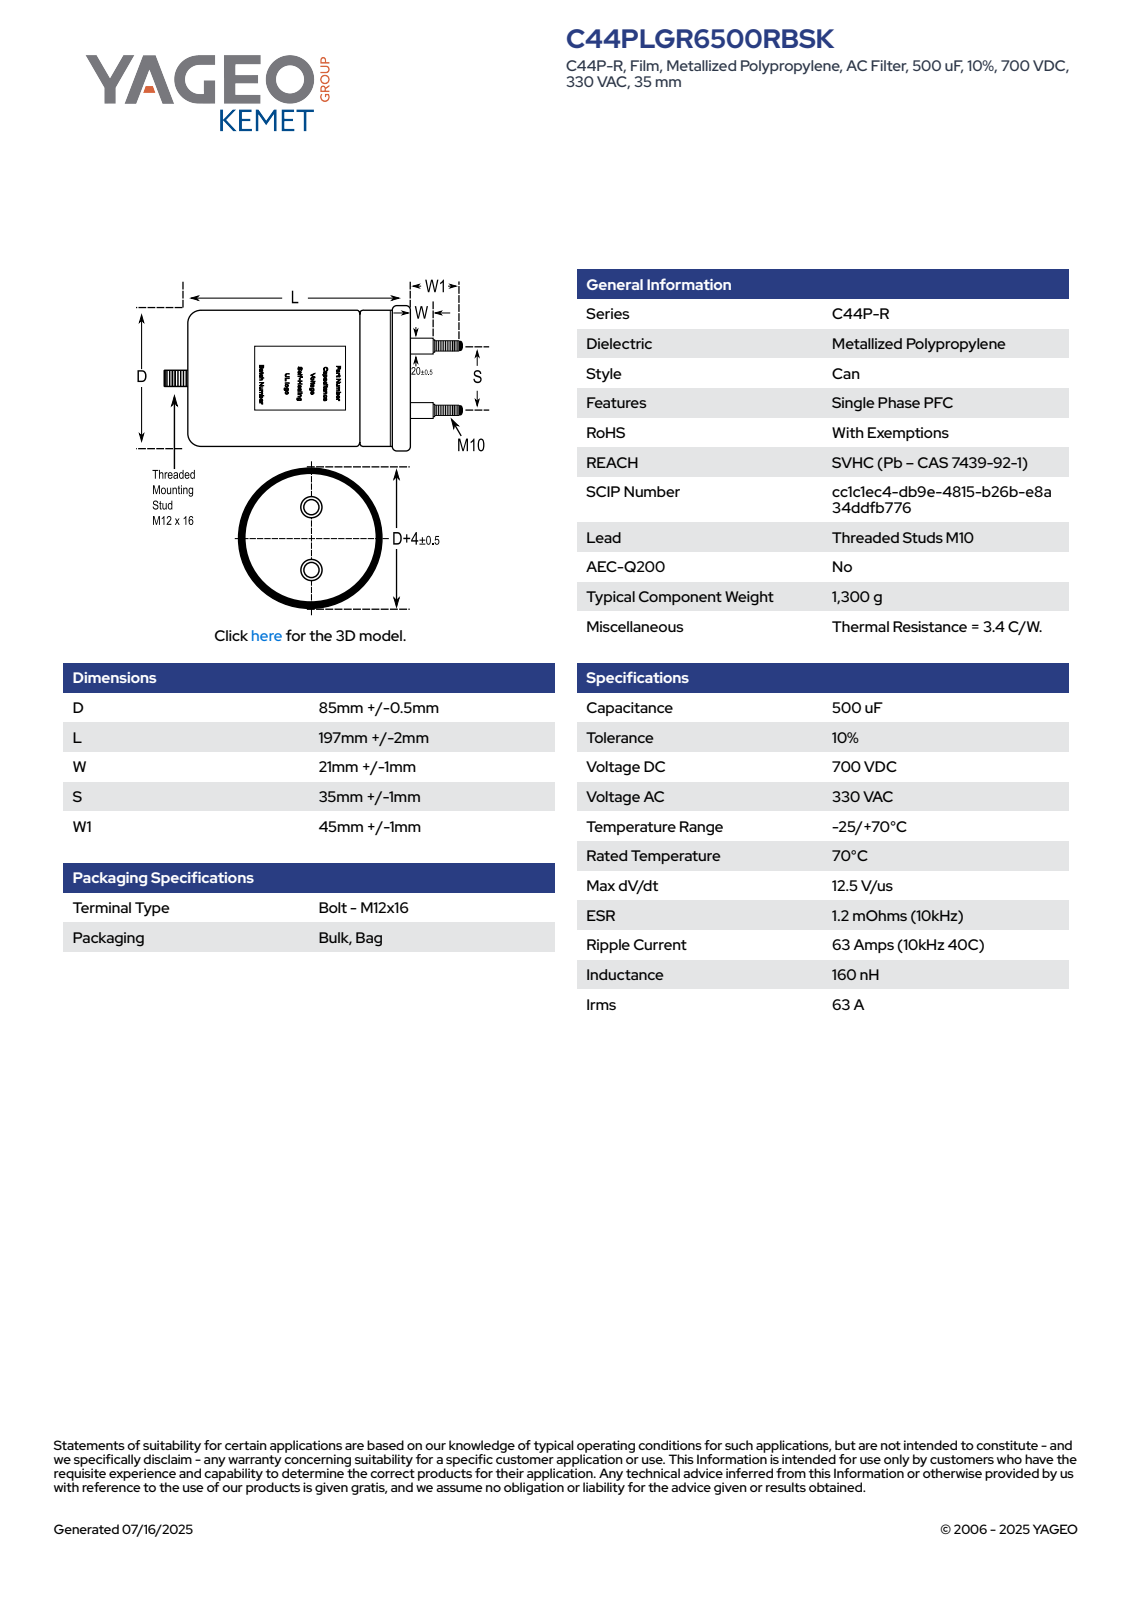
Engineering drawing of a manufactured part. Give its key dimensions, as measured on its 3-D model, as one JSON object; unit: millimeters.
{"part_name": "CFP_C44P_85X197_D85.5L199S35", "step_written_by": "SolidWorks 2014 (AUTOMOTIVE_DESIGN)", "units": "millimeters", "bodies": {"solids": 1, "faces": 105, "planar": 32, "cylindrical": 36, "other": 37}, "overall_size": [261, 90, 90], "volume_mm3": 1165000, "surface_area_mm2": 70330, "round_bosses_or_shafts": [[12, 3], [20.5, 2], [10, 2], [90, 1], [85.5, 1]], "partial_cylinders_radius": [[42.76, 1]], "face_to_face_distances": [199, 220, 21, 192.61, 6.39, 27.39, 245, 52.39, 46, 25]}
